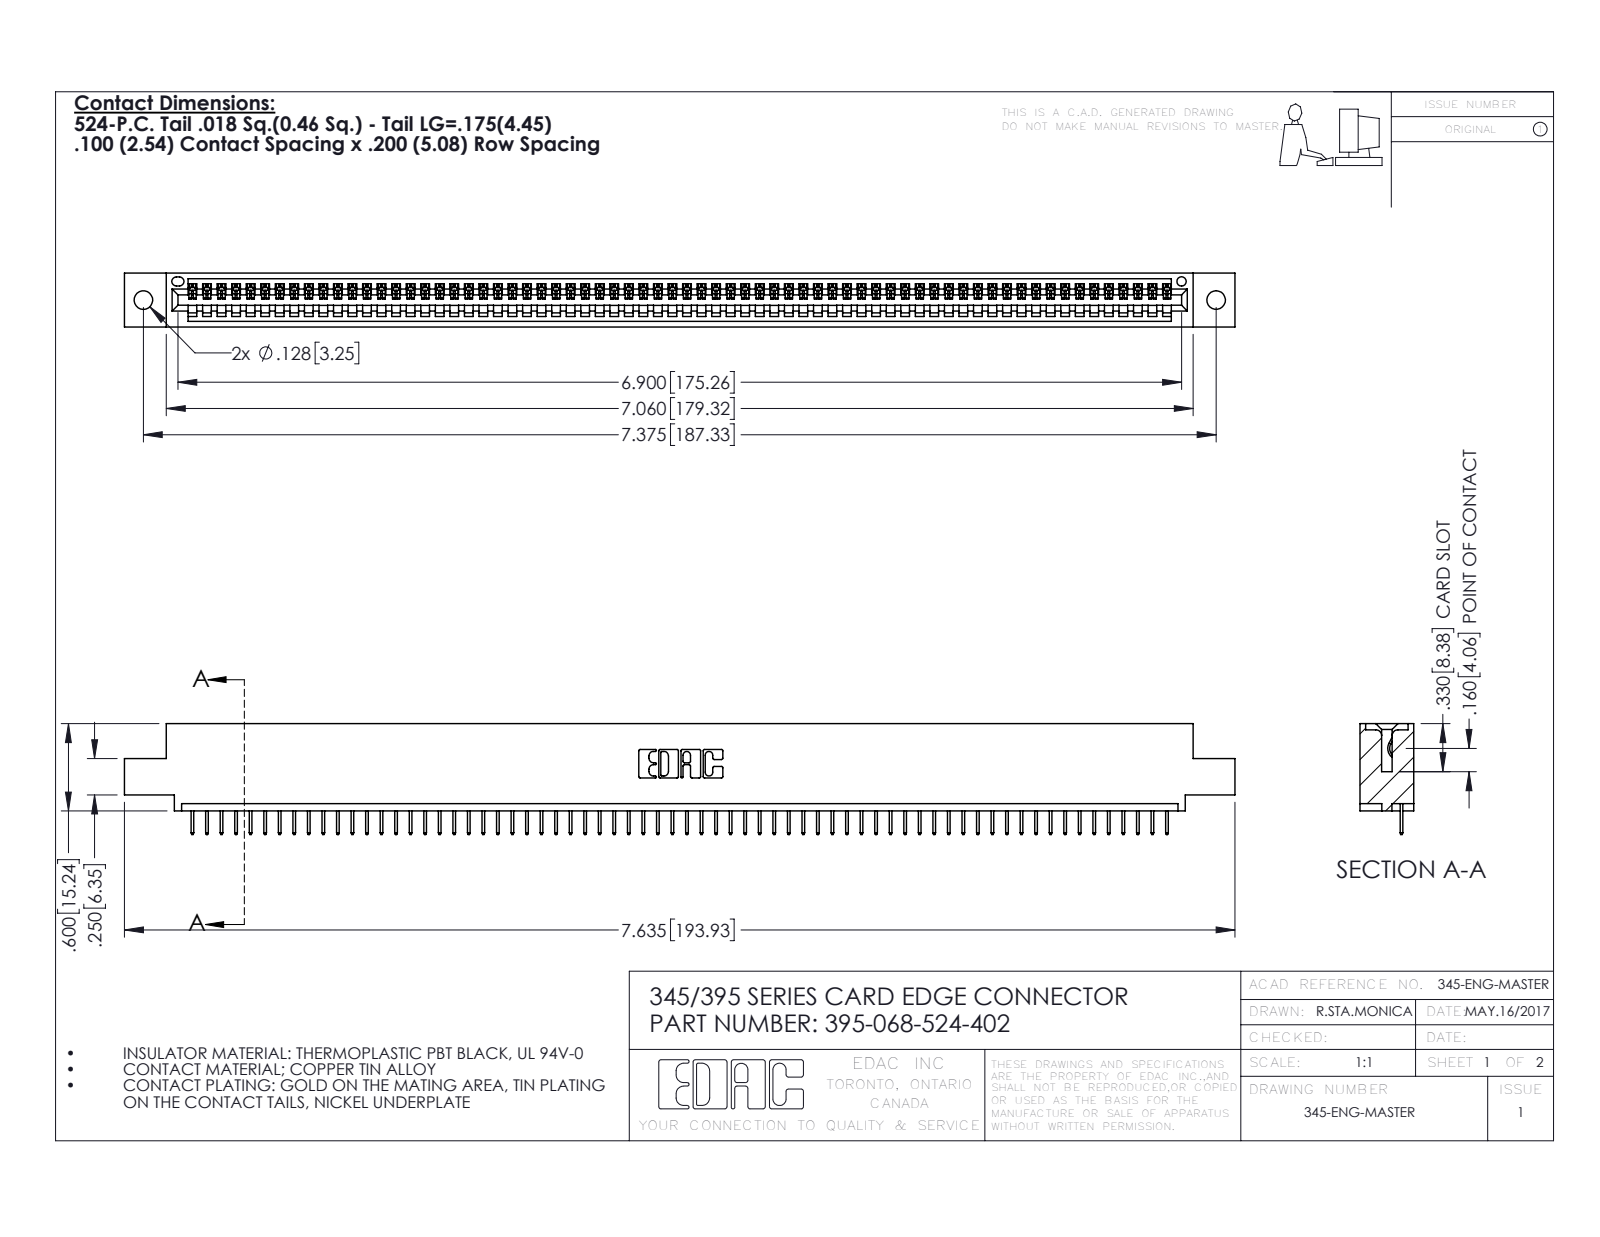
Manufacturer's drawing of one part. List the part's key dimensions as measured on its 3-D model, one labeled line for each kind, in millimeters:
Part name (STEP PRODUCT): 345 Part_0.110 Offset - 0.128 Dia; 345-292-001_345-293-124; 395-068-524-402
STEP written by: SolidWorks 2016 (CONFIG_CONTROL_DESIGN)
Units: millimetres
Bodies: 69 solids, 4346 faces (3212 planar, 1134 cylindrical, 0 other)
Overall size (bounding box): 193.9 × 19.4 × 9.4
Volume: 18 260 mm³ · Surface area: 23 560 mm²
Round holes (diameter × count): ⌀3.3 ×2, ⌀1.6 ×1
Partial cylindrical surfaces — rounded edges, fillets, slot ends (radius × count): R0.2 ×136, R0.3 ×22, R0.2 ×6, R0.8 ×6, R0.7 ×3, R0.8 ×2, R1 ×2, R0.4 ×1
Main face-to-face distances: 1.8, 7.6, 9.4, 5.1, 2.5, 6.9, 0.6, 5.7, 1.8, 3.8
Hole centre spacings: 6.9, 181.3, 187.3
